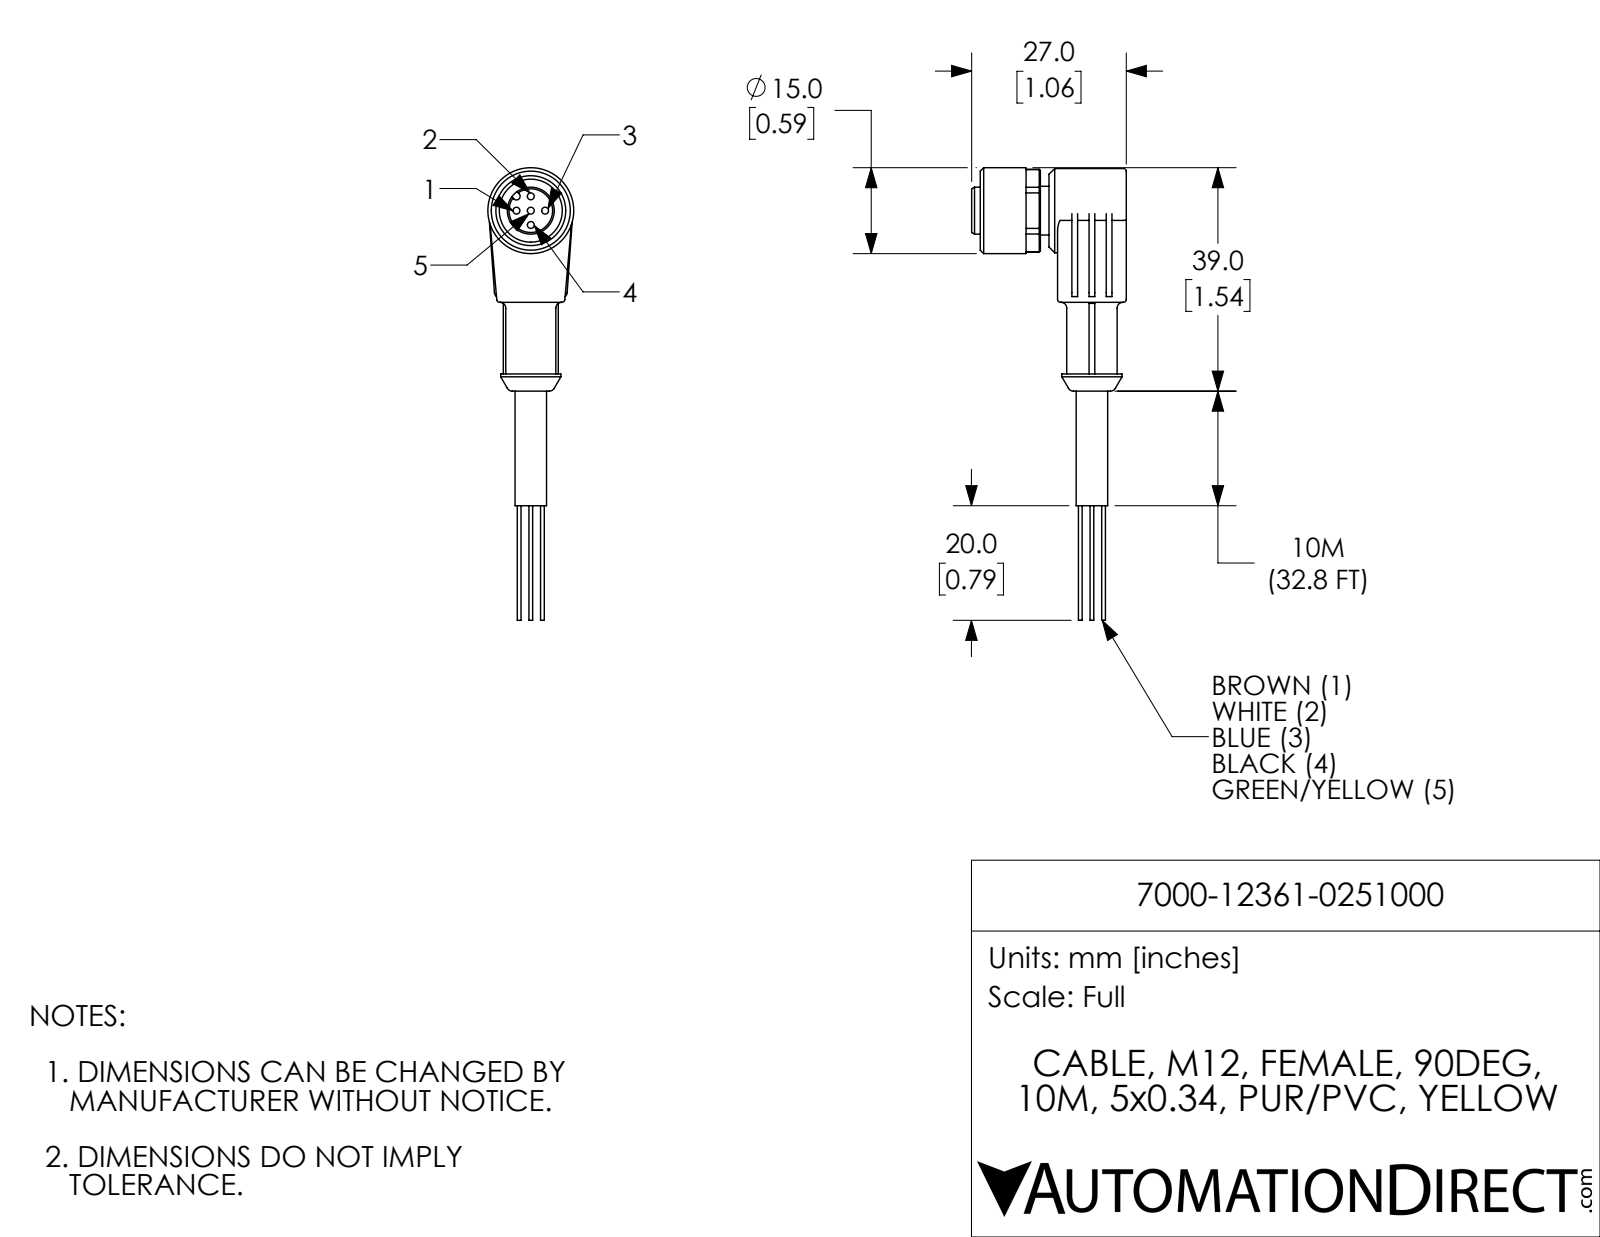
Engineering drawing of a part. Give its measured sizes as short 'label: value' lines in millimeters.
name: 7000-12361-0251000
written by: SolidWorks 2017 (AUTOMOTIVE_DESIGN)
unit: mm
bodies: 1 solid, 155 faces (66 planar, 61 cylindrical, 28 other)
size: 79 × 27 × 15
volume: 6 830 mm³; area: 3 817 mm²
holes: 5× ⌀1.2, 1× ⌀4.8, 1× ⌀11
bosses: 5× ⌀0.7, 1× ⌀15, 1× ⌀14.7, 1× ⌀10.5, 1× ⌀8.8, 1× ⌀8.5, 1× ⌀8.2, 1× ⌀5.5
rounds: 8× R0.5, 2× R1, 1× R0.7, 1× R7.2
face distances: 12, 1.5, 3, 13.5, 15, 5.5, 9.5, 6, 8, 12.5
hole spacings: 2.5, 3.5, 5
